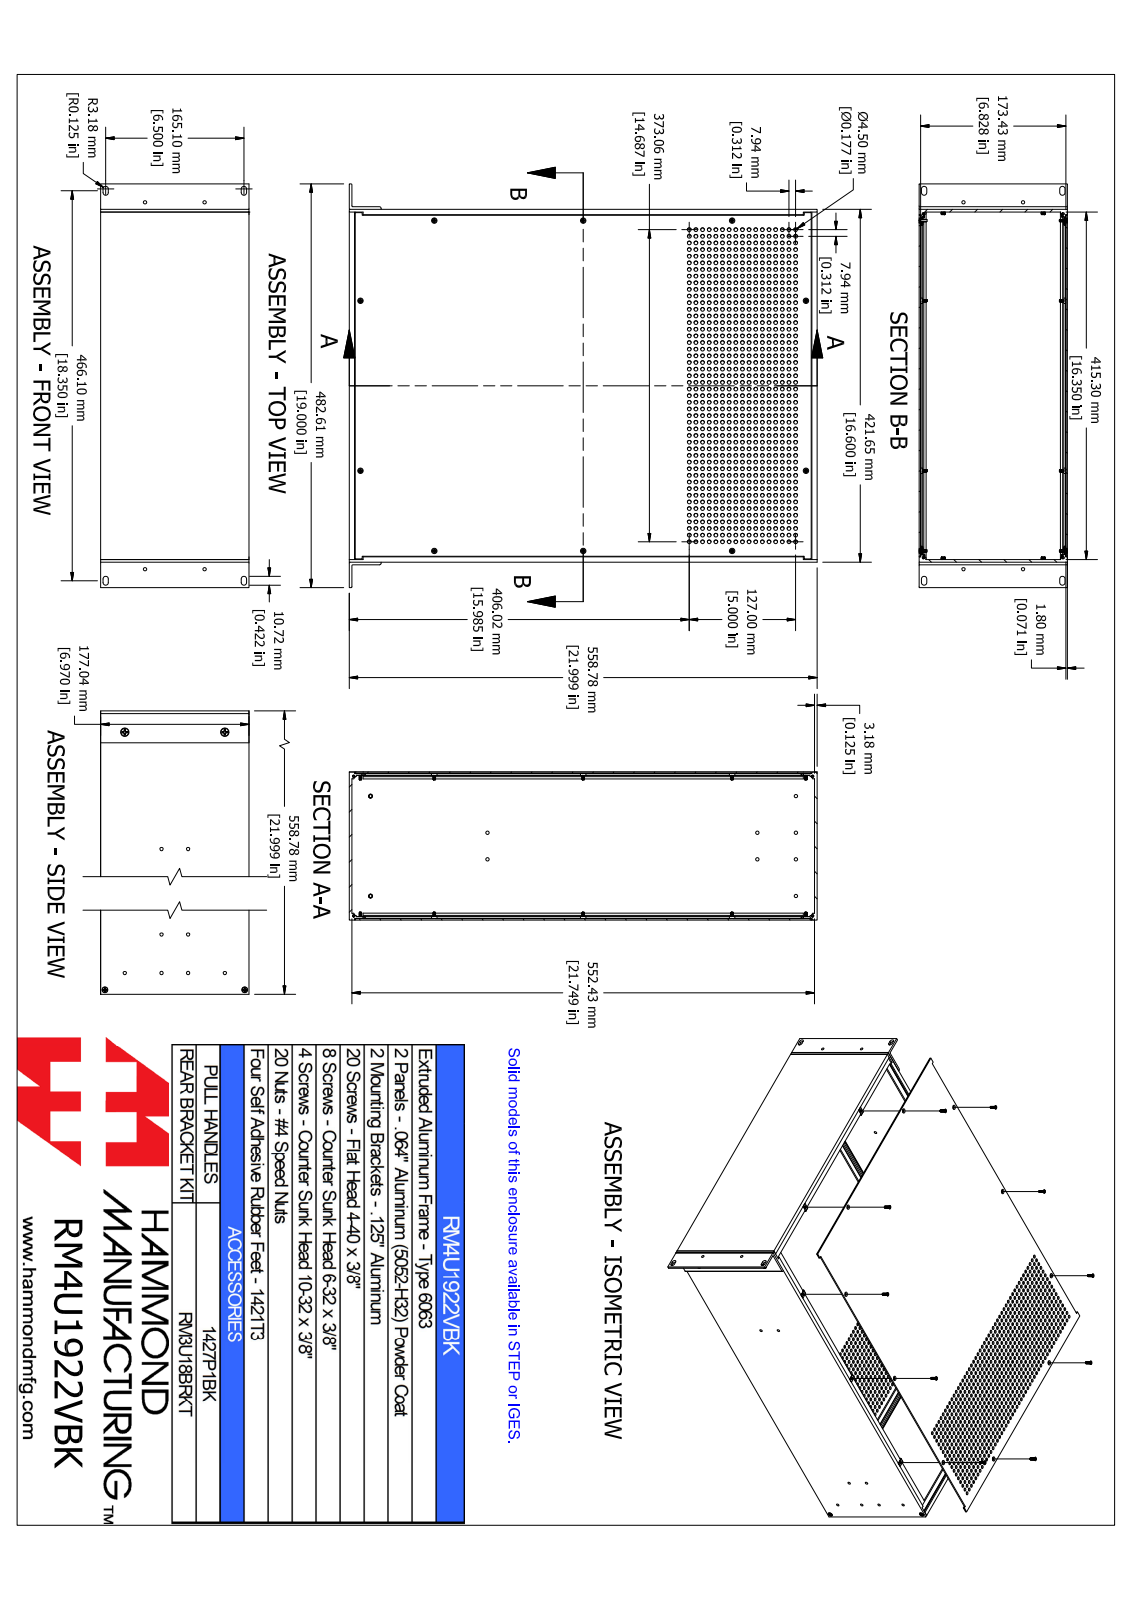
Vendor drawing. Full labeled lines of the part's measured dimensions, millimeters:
Part name (STEP PRODUCT): RM4U1922VBK
STEP written by: SolidWorks 2021 (AUTOMOTIVE_DESIGN)
Units: millimetres
Bodies: 60 solids, 3916 faces (952 planar, 2176 cylindrical, 788 other)
Overall size (bounding box): 558.8 × 482.6 × 177.1
Volume: 2 083 000 mm³ · Surface area: 1 770 000 mm²
Round holes (diameter × count): ⌀4.5 ×1632, ⌀4 ×10, ⌀4.1 ×10, ⌀4 ×6, ⌀4.2 ×6, ⌀3.5 ×4, ⌀4 ×4, ⌀4 ×4, ⌀4.3 ×4, ⌀5 ×2
Round bosses / shafts (diameter × count): ⌀5.1 ×10, ⌀2.8 ×10, ⌀6 ×5, ⌀3.5 ×5, ⌀9.1 ×2, ⌀4.8 ×2
Partial cylindrical surfaces — rounded edges, fillets, slot ends (radius × count): R0.3 ×80, R0.6 ×80, R0.2 ×40, R0.4 ×40, R0.4 ×16, R1 ×16, R1 ×14, R0.9 ×9
Main face-to-face distances: 1.8, 175.2, 177, 173.4, 418.5, 3.2, 3.2, 555.6, 421.7, 415.3
Hole centre spacings: 177.8, 130.2, 433, 31.8, 203.2, 282.7, 311.8, 355.6
